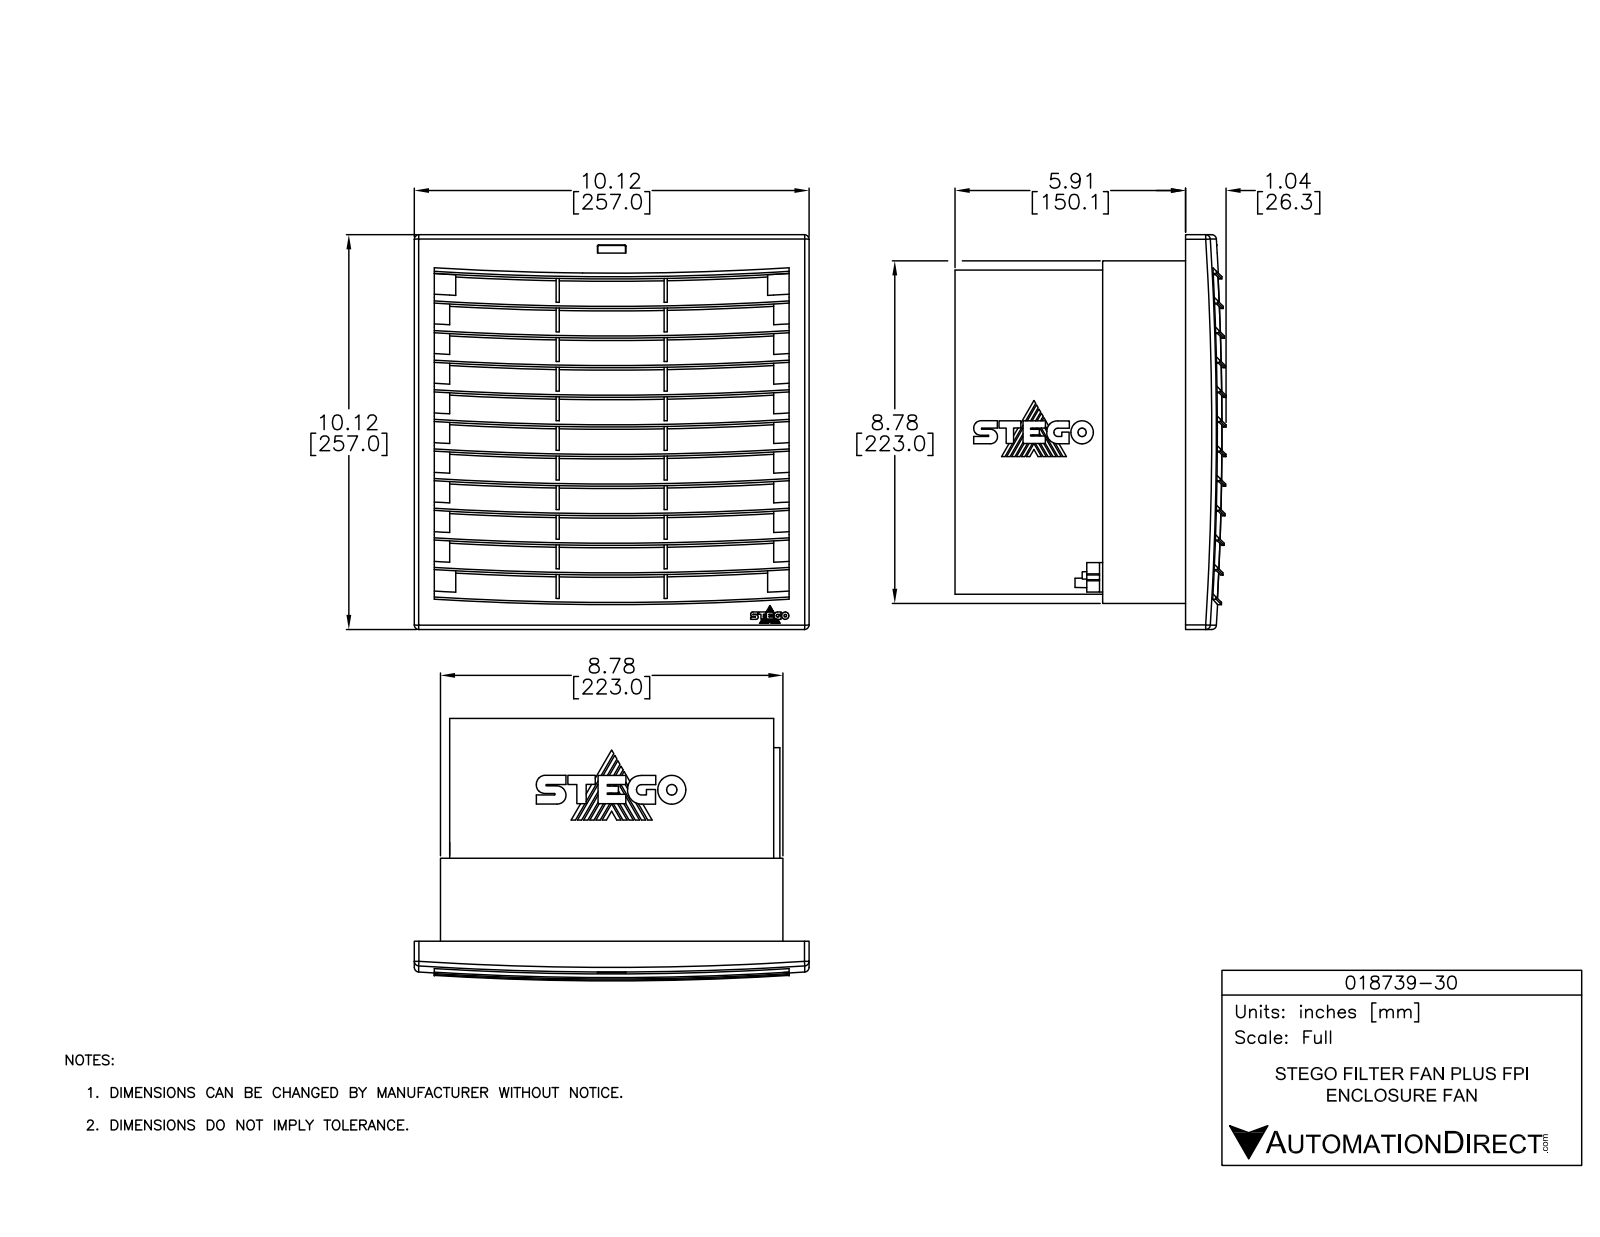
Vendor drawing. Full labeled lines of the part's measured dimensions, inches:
Part name (STEP PRODUCT): 018739-30
STEP written by: SolidWorks 2018 (AUTOMOTIVE_DESIGN)
Units: inches
Bodies: 1 solid, 814 faces (468 planar, 346 cylindrical, 0 other)
Overall size (bounding box): 10.118 × 10.118 × 6.811
Volume: 192.8 in³ · Surface area: 1 039 in²
Round holes (diameter × count): ⌀2.268 ×1, ⌀3.018 ×1, ⌀3.769 ×1, ⌀4.487 ×1, ⌀4.52 ×1, ⌀5.27 ×1, ⌀5.42 ×1, ⌀6.021 ×1, ⌀6.353 ×1, ⌀6.929 ×1, ⌀7.463 ×1
Round bosses / shafts (diameter × count): ⌀8.64 ×1, ⌀8.228 ×1, ⌀8.146 ×1, ⌀6.707 ×1, ⌀6.336 ×1, ⌀5.774 ×1, ⌀5.585 ×1, ⌀4.841 ×1
Partial cylindrical surfaces — rounded edges, fillets, slot ends (radius × count): R42.577 ×21, R3.361 ×5, R0.197 ×4, R0.26 ×4, R0.933 ×1, R1.311 ×1, R1.488 ×1, R1.777 ×1
Main face-to-face distances: 0.536, 0.059, 0.543, 2.145, 2.681, 1.609, 0.22, 8.56, 1.073, 1.072
